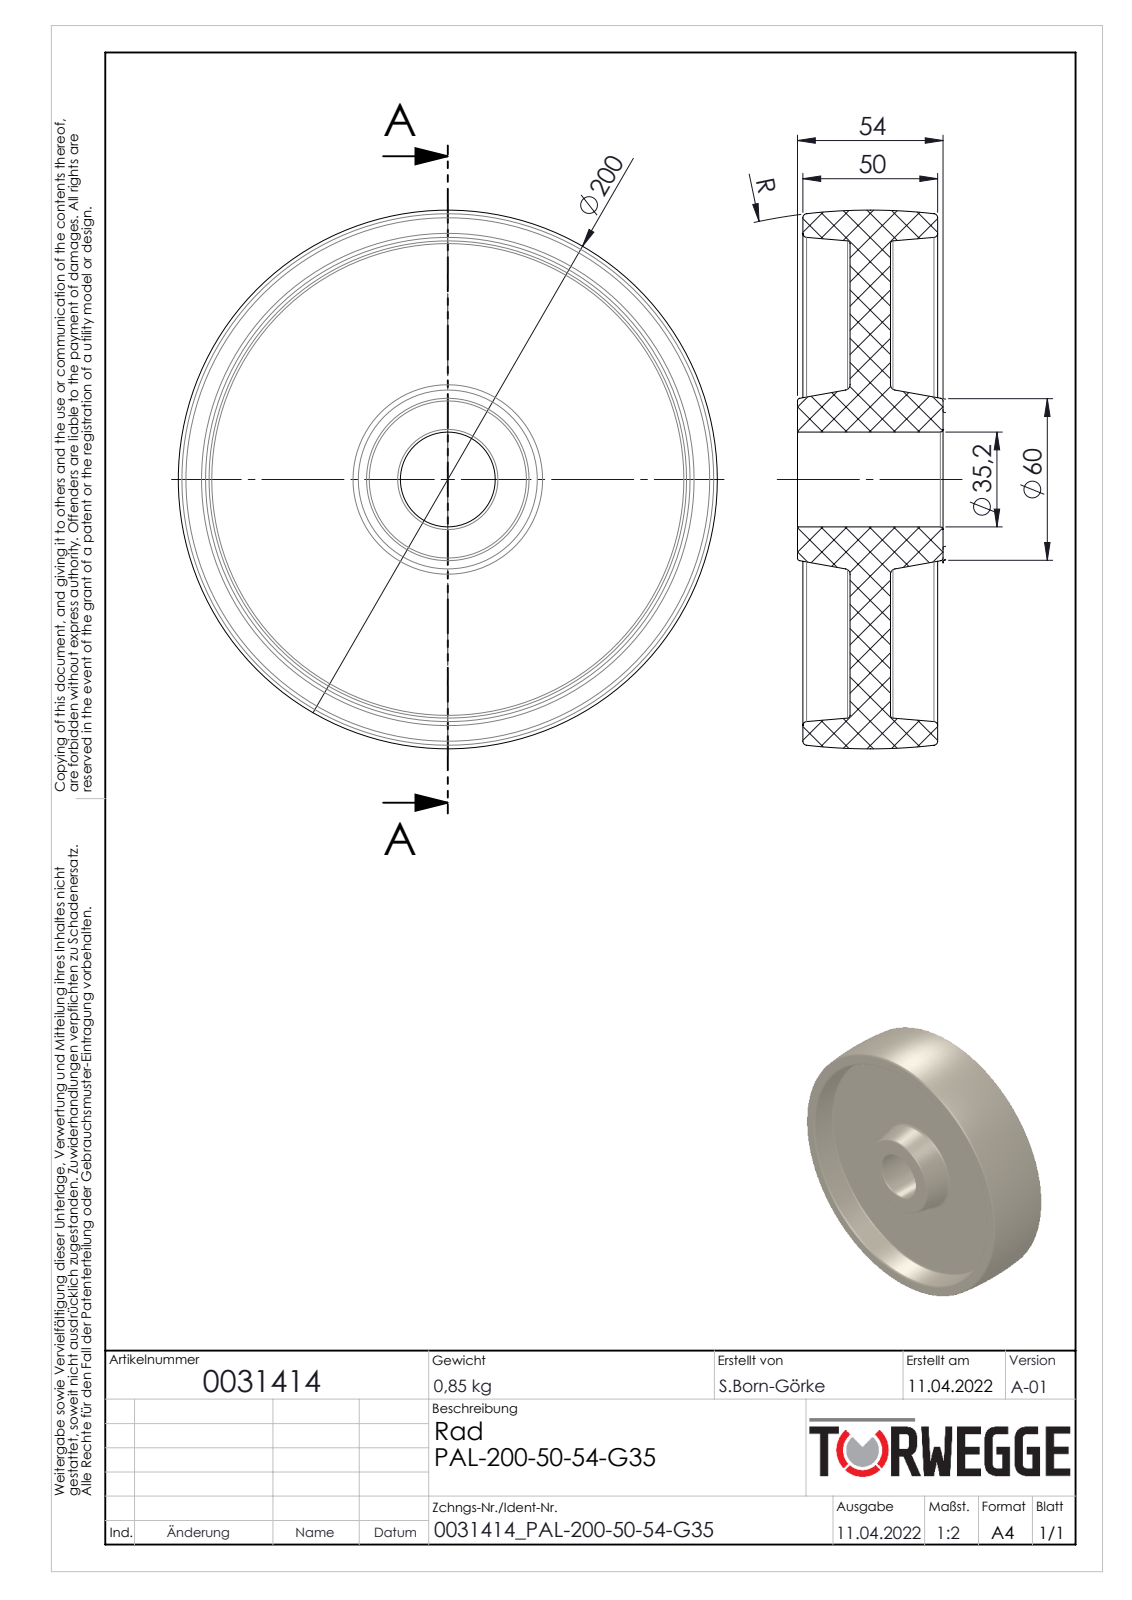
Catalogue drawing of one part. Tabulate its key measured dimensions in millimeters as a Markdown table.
| quantity | value |
| --- | --- |
| part name | 0031414 |
| STEP written by | SolidWorks 2020 (AUTOMOTIVE_DESIGN) |
| units | millimeters |
| bodies | 1 solid, 42 faces (6 planar, 2 cylindrical, 34 other) |
| overall size | 200 × 200 × 54 |
| volume | 750 202 mm³ |
| surface area | 118 879 mm² |
| round holes (diameter × count) | 35.2 × 1 |
| main face-to-face distances | 15, 17.5, 32.5, 50, 2, 19.5, 34.5, 52, 54 |
